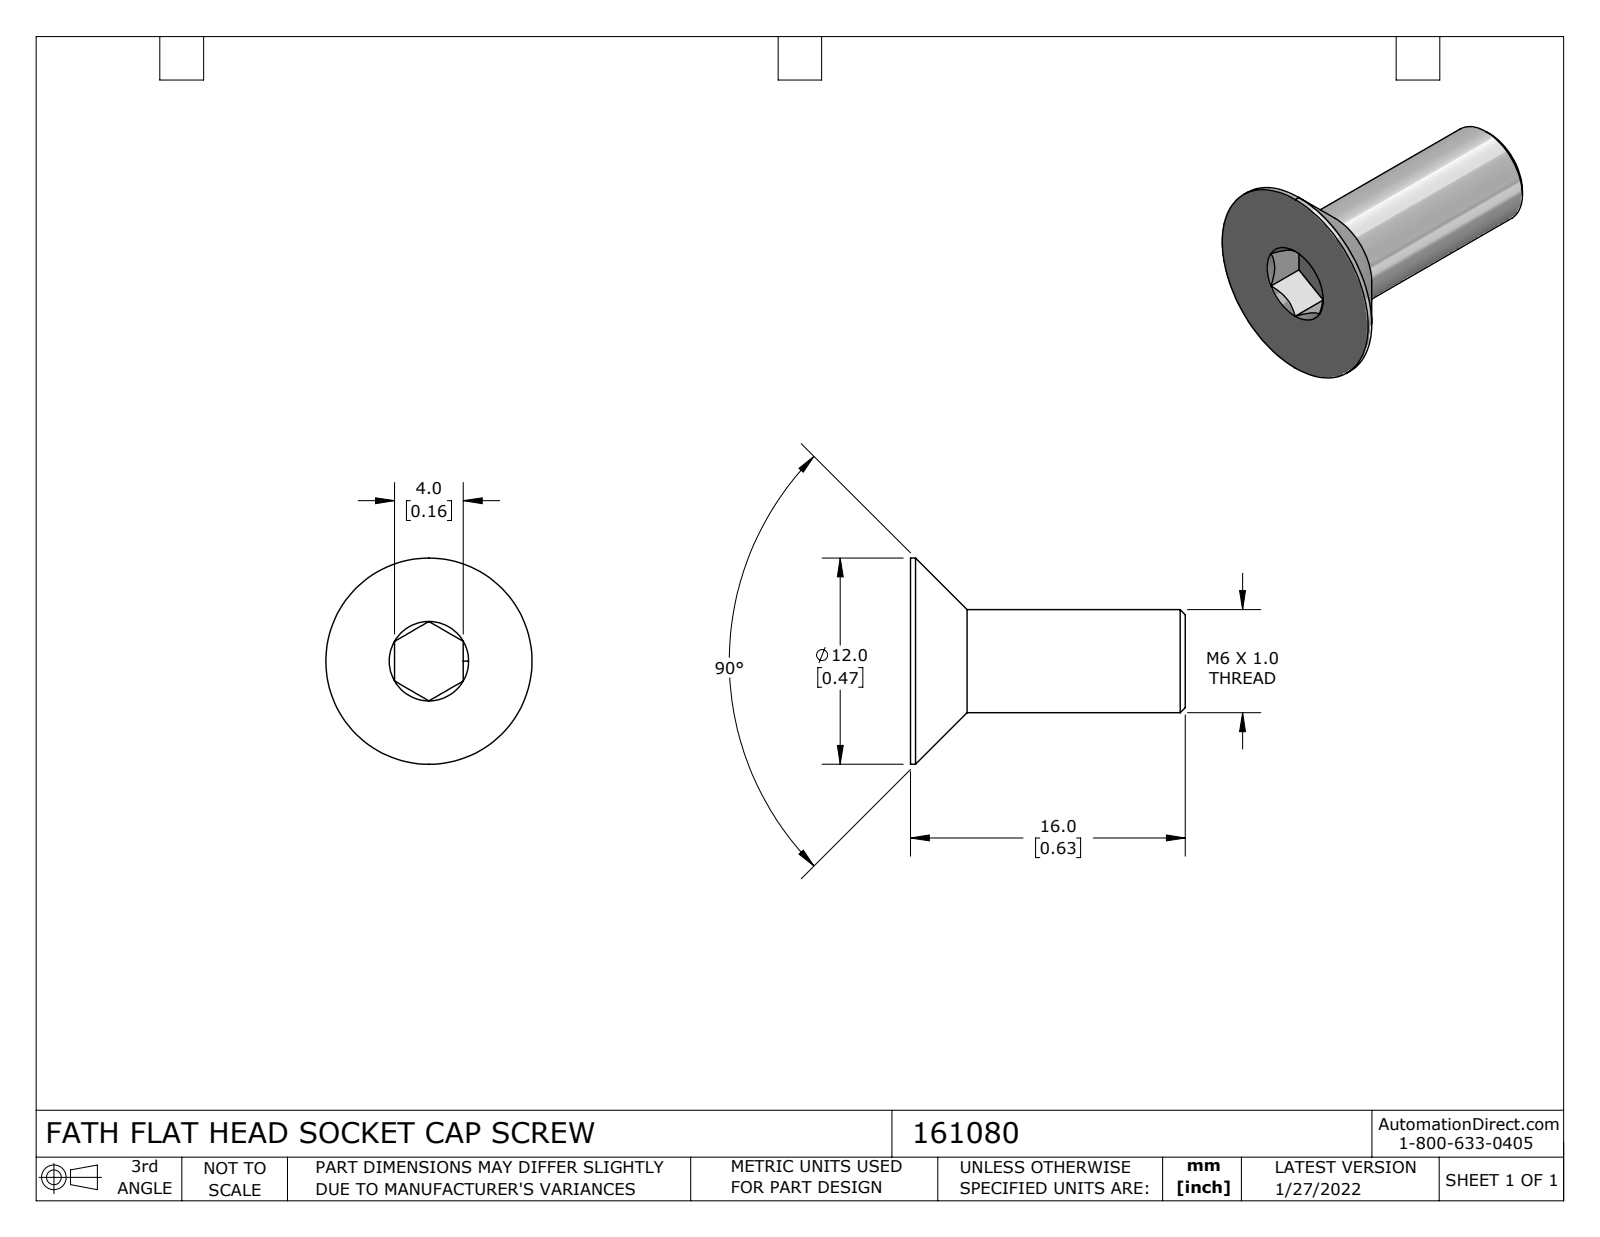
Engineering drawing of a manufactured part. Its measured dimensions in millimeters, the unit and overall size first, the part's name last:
Units: millimetres
Overall size (bounding box): 16 × 12 × 12
Round bosses / shafts (diameter × count): ⌀12 ×1, ⌀6 ×1
Main face-to-face distances: 16, 4, 13.69, 2.31
Volume: 558 mm³ · Surface area: 539 mm²
Bodies: 1 solid, 24 faces (9 planar, 4 cylindrical, 11 other)
Part name (STEP PRODUCT): 161080
STEP written by: SolidWorks 2021 (CONFIG_CONTROL_DESIGN)
